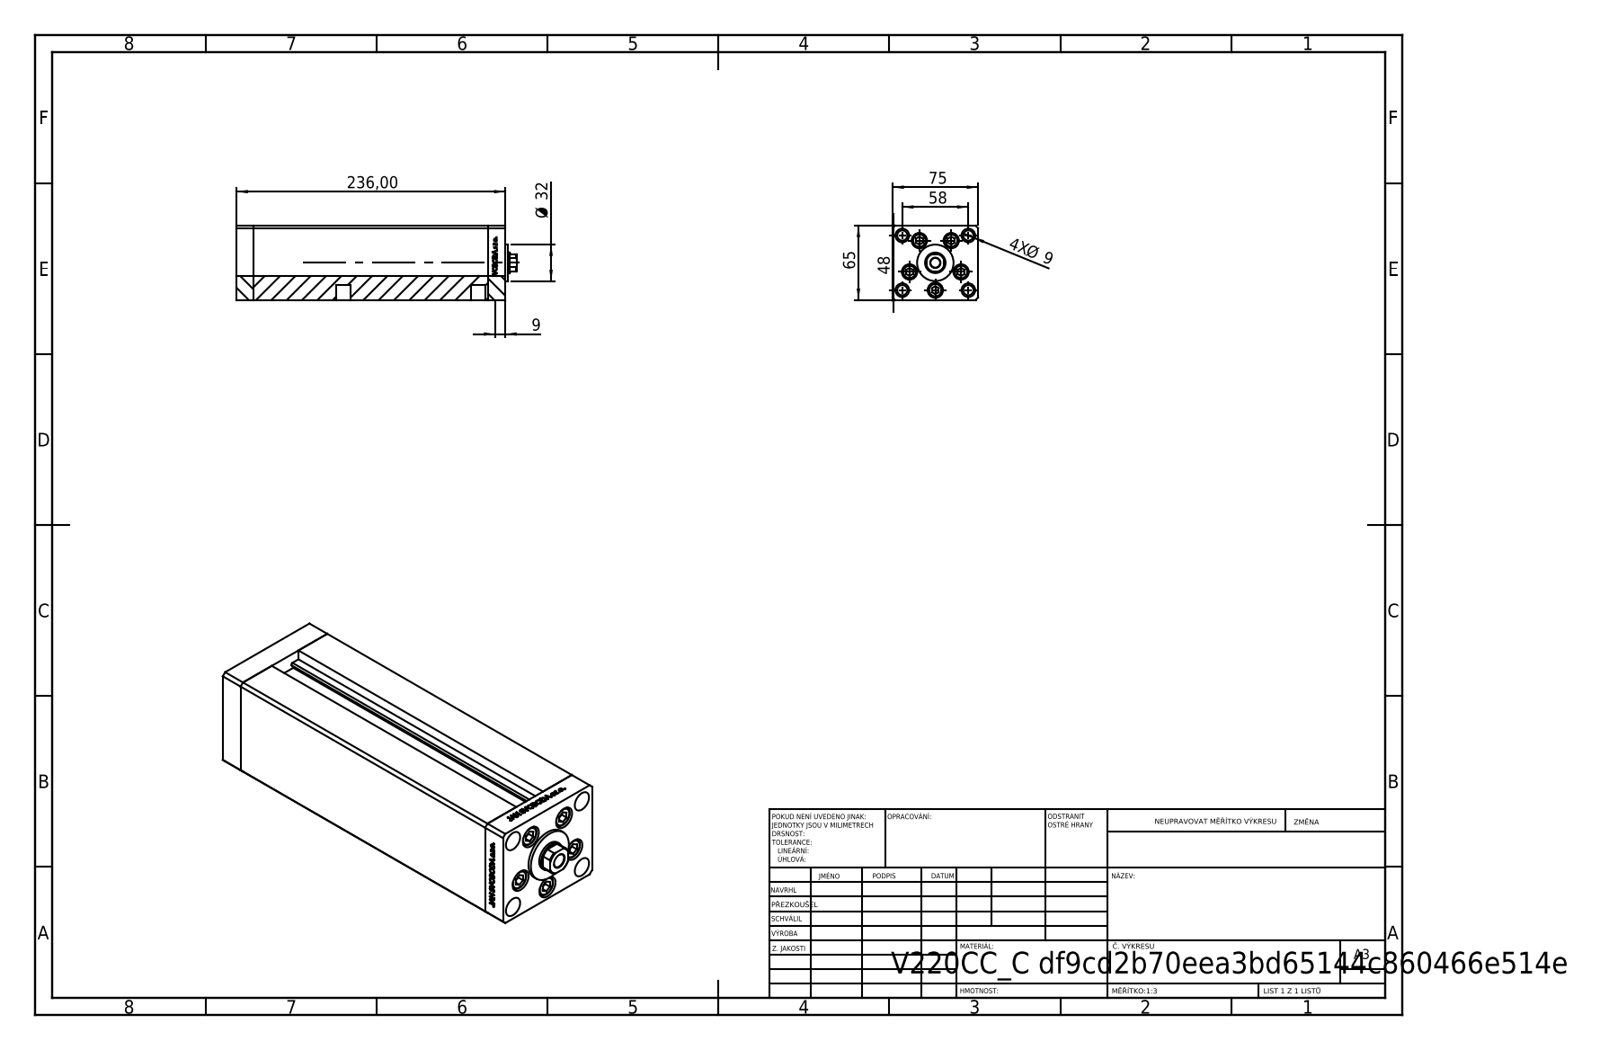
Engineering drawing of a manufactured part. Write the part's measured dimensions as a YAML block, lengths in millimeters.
part_name: "V220C_C MIDDLE; V220C_VC_C; ALLEN BOLT; V220C BACK_C (+1 more)"
step_written_by: "SolidWorks 2019 (CONFIG_CONTROL_DESIGN)"
units: millimeters
bodies: {solids: 13, faces: 1183, planar: 546, cylindrical: 175, other: 462}
overall_size: [246, 75, 65]
volume: 958443
surface_area: 179366
round_holes:
  - {diameter: 9, count: 9}
  - {diameter: 13.5, count: 5}
  - {diameter: 2, count: 4}
  - {diameter: 8, count: 4}
  - {diameter: 12, count: 4}
  - {diameter: 13.16, count: 4}
  - {diameter: 8.5, count: 1}
  - {diameter: 12.5, count: 1}
  - {diameter: 18, count: 1}
round_bosses_or_shafts:
  - {diameter: 8, count: 5}
  - {diameter: 12.5, count: 4}
  - {diameter: 32, count: 1}
partial_cylinders:
  - {radius: 0.93, count: 2}
  - {radius: 8.5, count: 1}
face_to_face_distances: [75, 65, 15, 206, 221, 236, 54.5, 10.5, 26.25, 48.75]
hole_center_spacings: [24, 37.64, 15.67, 17.22, 27.71, 28.83, 29, 32.63]
